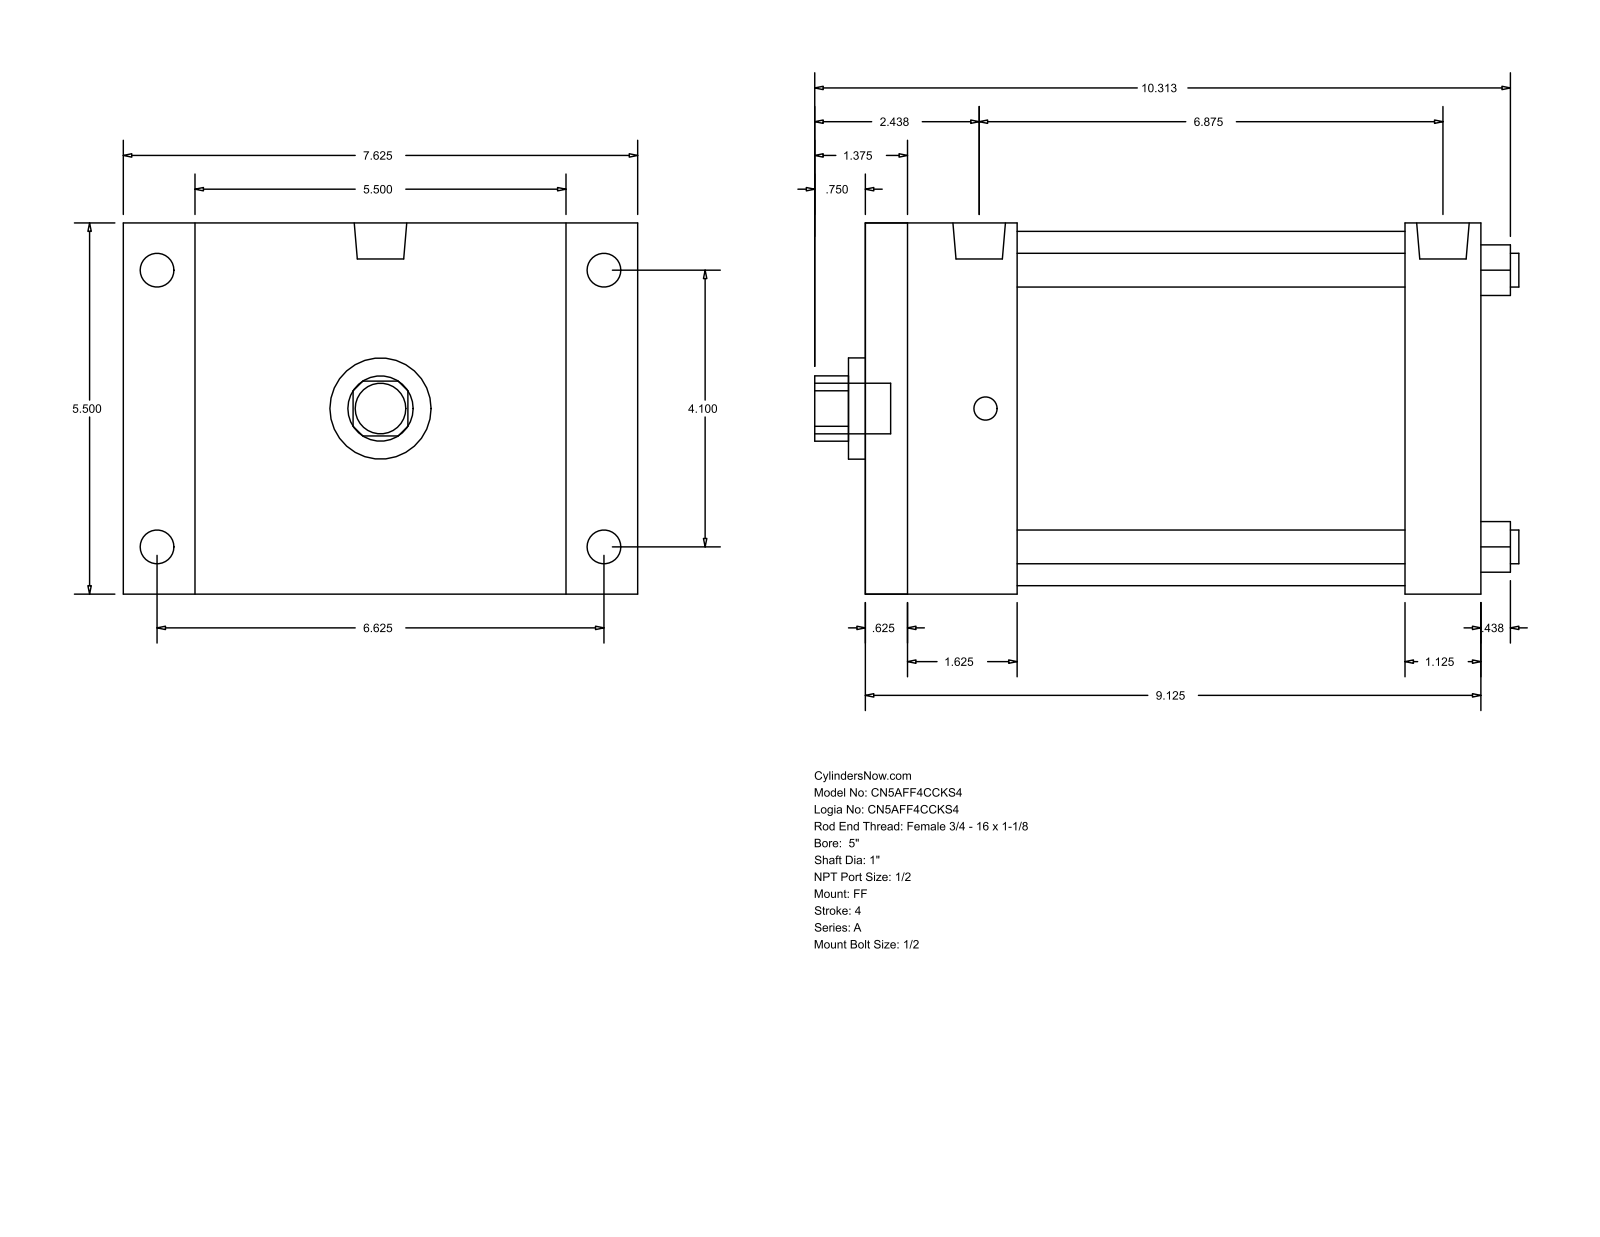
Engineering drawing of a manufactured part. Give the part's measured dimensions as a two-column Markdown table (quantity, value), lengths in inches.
| quantity | value |
| --- | --- |
| part name | A_FF__0500_1 |
| STEP written by | GSSL Pune (CONFIG_CONTROL_DESIGN) |
| units | inches |
| bodies | 0 solids, 92 faces (64 planar, 28 cylindrical, 0 other) |
| overall size | 10.437 × 7.625 × 5.5 |
| round holes (diameter × count) | 0.5 × 4, 1 × 1, 1.5 × 1, 5.25 × 1 |
| round bosses / shafts (diameter × count) | 0.5 × 4, 0.344 × 4, 0.778 × 2, 0.75 × 1 |
| partial cylindrical surfaces (radius × count) | 0.484 × 1 |
| main face-to-face distances | 5.5, 9.125, 0.625, 8.5, 1.125, 8, 7.375, 2.25, 1.625, 5.75 |
| hole center spacings | 2.899, 4.1, 5.798 |
